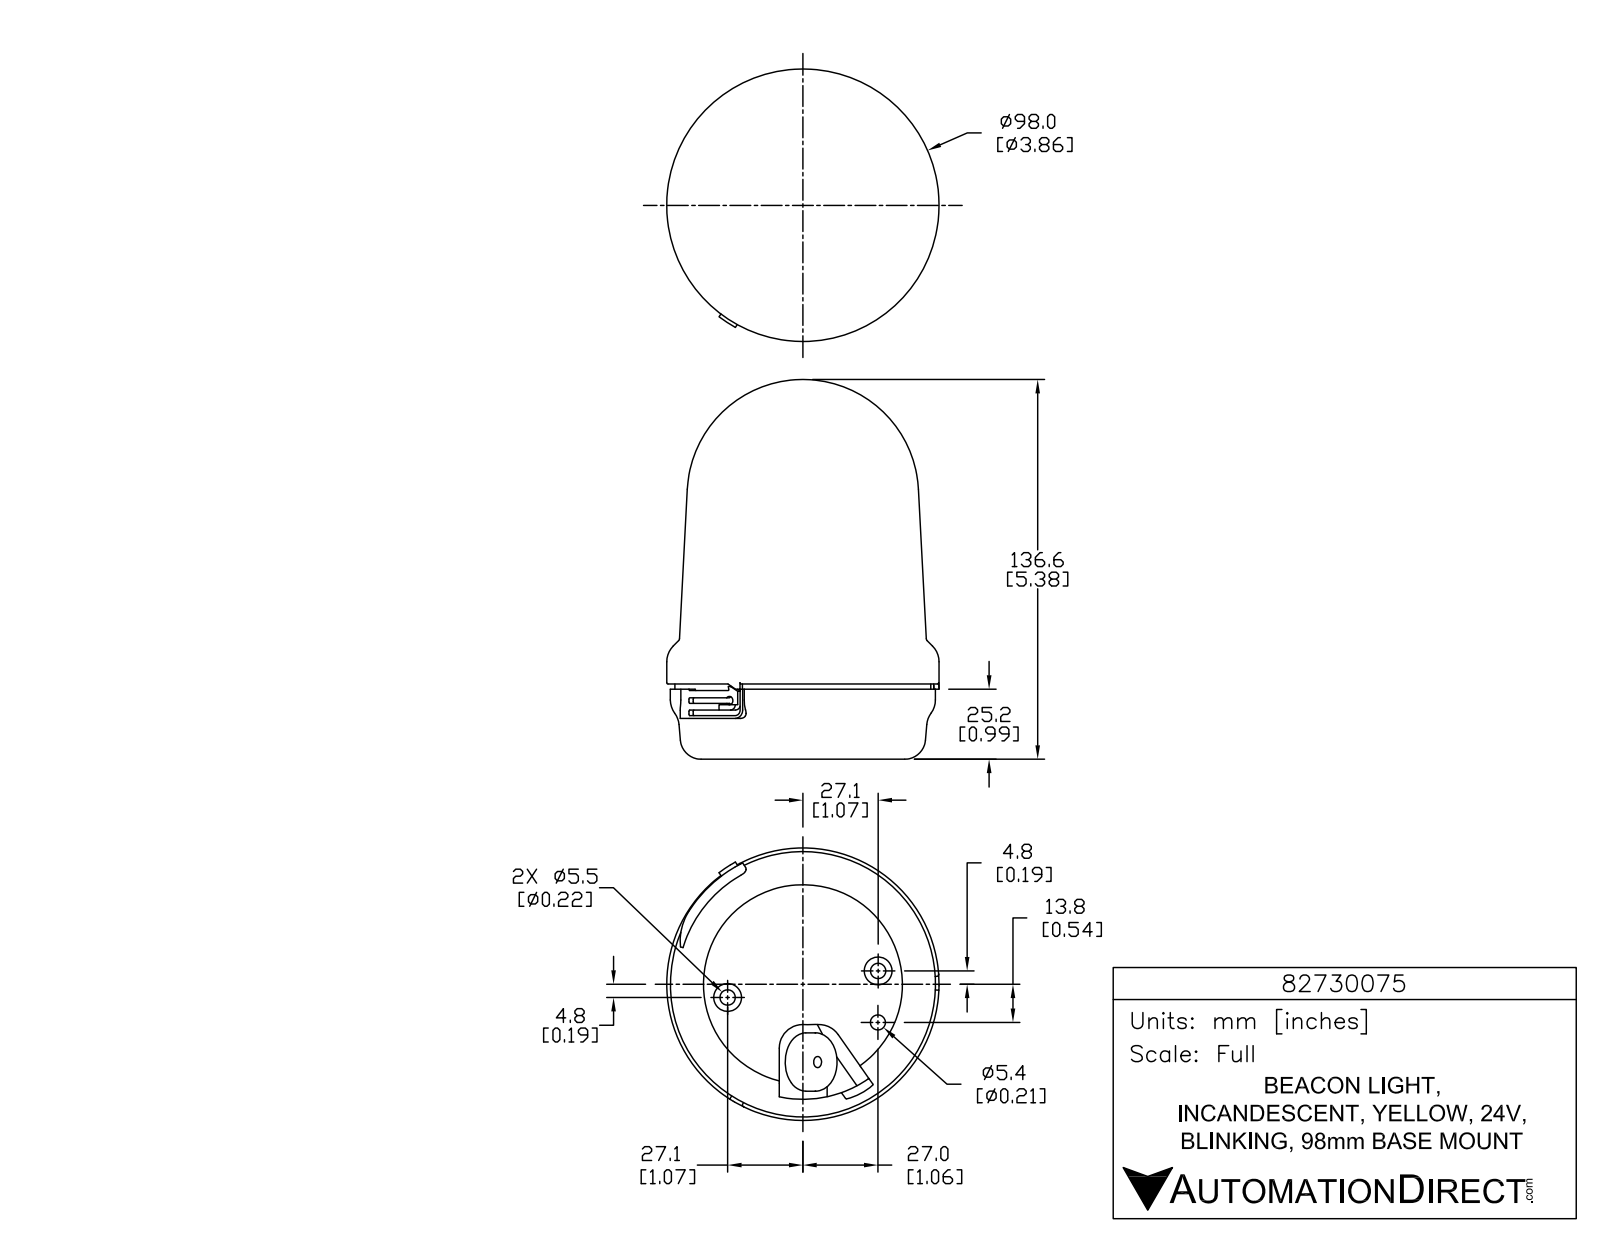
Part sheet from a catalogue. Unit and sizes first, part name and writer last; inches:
Units: inches
Overall size (bounding box): 5.378 × 3.858 × 3.858
Round holes (diameter × count): ⌀0.059 ×3, ⌀0.217 ×2, ⌀0.157 ×1, ⌀0.213 ×1, ⌀2.819 ×1
Round bosses / shafts (diameter × count): ⌀0.339 ×3, ⌀0.084 ×3, ⌀0.394 ×2, ⌀3.858 ×1, ⌀3.756 ×1, ⌀3.626 ×1, ⌀0.827 ×1
Partial cylindrical surfaces — rounded edges, fillets, slot ends (radius × count): R0.005 ×9, R0.005 ×6, R0.012 ×6, R0.012 ×6, R0.012 ×6, R0.196 ×6, R0.02 ×5, R0.039 ×4
Main face-to-face distances: 1.045, 0.972, 0.073, 0.02, 0.992, 1.065, 0.236, 0.579, 0.559, 0.413
Hole centre spacings: 1.083, 0.73, 1.193, 2.158, 2.165
Volume: 44.69 in³ · Surface area: 73.66 in²
Bodies: 1 solid, 872 faces (566 planar, 204 cylindrical, 102 other)
Part name (STEP PRODUCT): 82730075
STEP written by: SolidWorks 2015 (AUTOMOTIVE_DESIGN)
